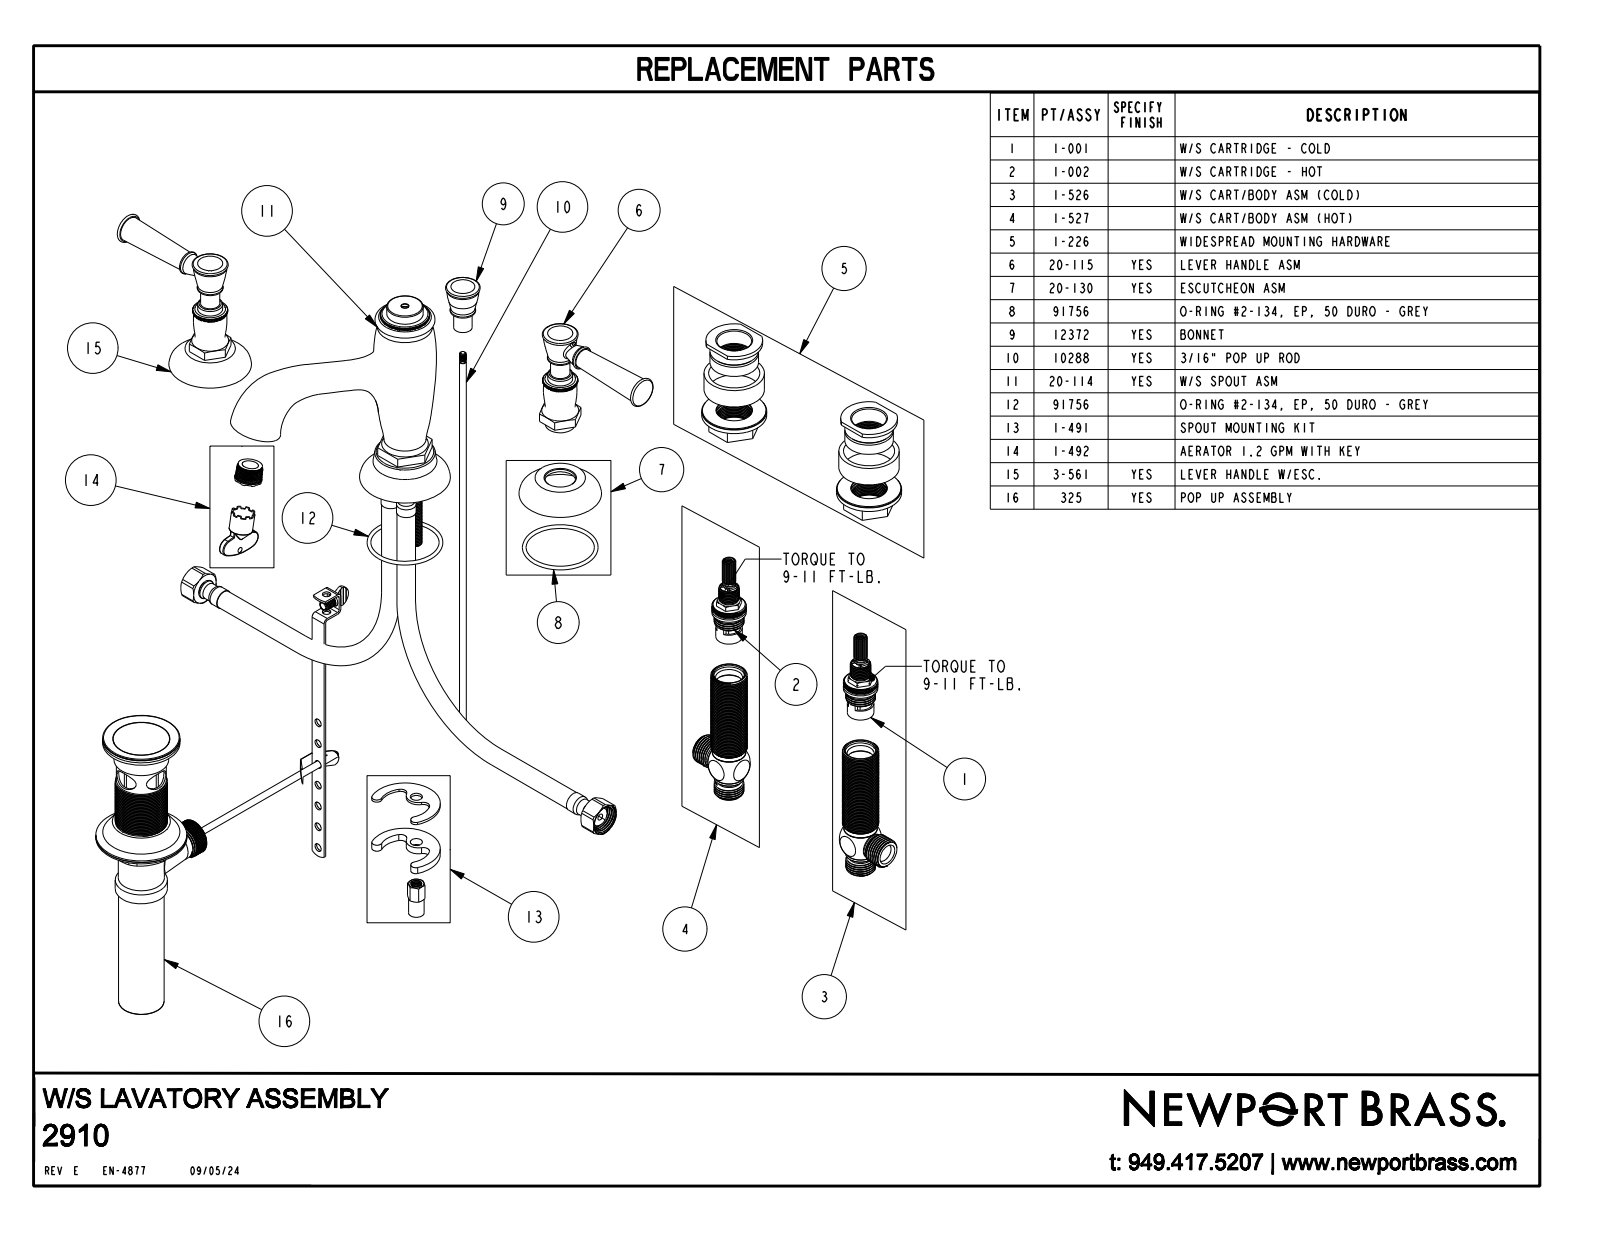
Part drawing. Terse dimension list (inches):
name: 12370_1_1_1_1; 40553_1_1_1_1; ASM0002_ASM
written by: CREO PARAMETRIC BY PTC INC, 2018400 (CONFIG_CONTROL_DESIGN)
unit: in
bodies: 3 solids, 1051 faces (630 planar, 40 cylindrical, 381 other)
size: 14.512 × 7.629 × 7.144
volume: 24.86 in³; area: 110.3 in²
holes: 1× ⌀0.738
bosses: 2× ⌀0.98, 2× ⌀0.686, 2× ⌀0.53, 1× ⌀1.12, 1× ⌀1, 1× ⌀0.75, 1× ⌀0.51
rounds: 2× R0.28
face distances: 0.534, 0.85, 0.316, 2.28, 3.623, 1.025, 3.305, 4.648, 6.928, 1.343
